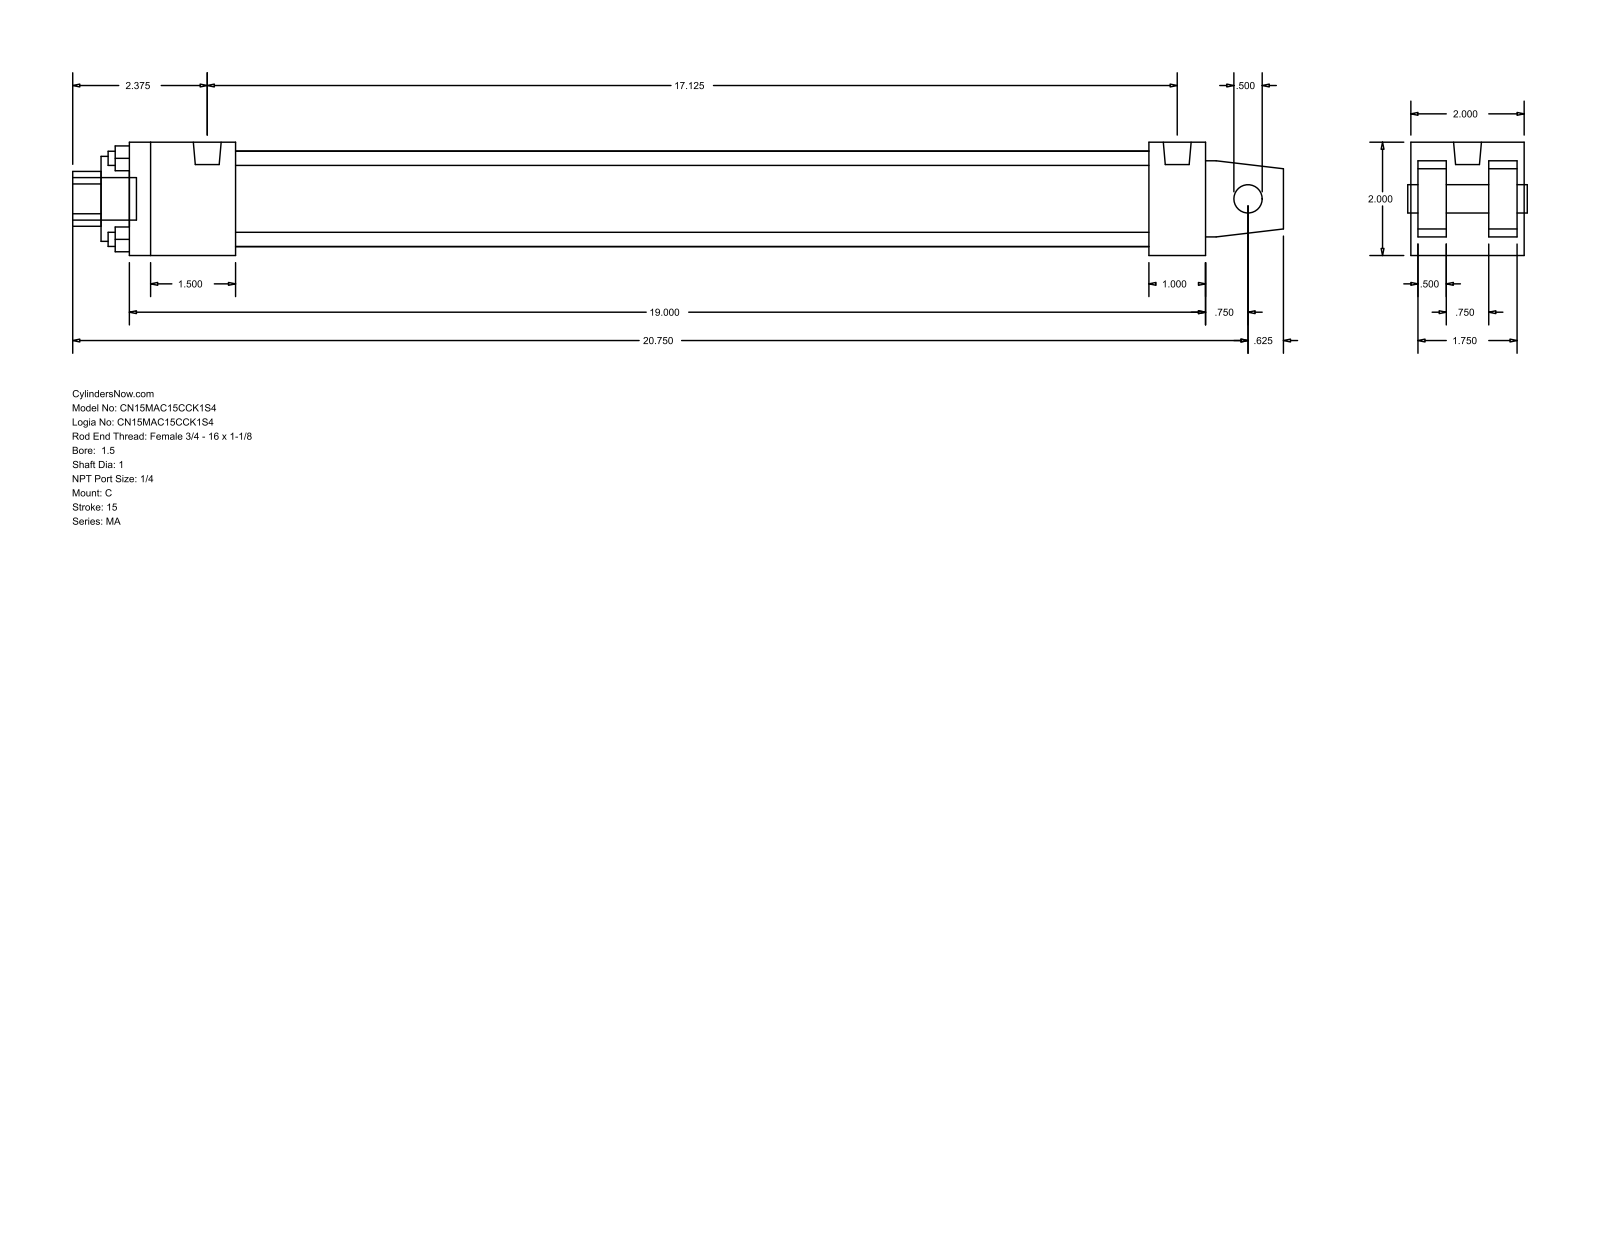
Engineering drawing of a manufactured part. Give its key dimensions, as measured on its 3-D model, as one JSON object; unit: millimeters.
{"part_name": "MA_C__0150_1", "step_written_by": "GSSL Pune (CONFIG_CONTROL_DESIGN)", "units": "millimeters", "bodies": {"solids": 0, "faces": 103, "planar": 76, "cylindrical": 27, "other": 0}, "overall_size": [542.92, 50.8, 50.8], "round_holes": [[6.35, 4], [12.7, 1], [25.4, 1], [38.1, 1], [42.93, 1]], "round_bosses_or_shafts": [[7.94, 4], [12.49, 2], [19.05, 1]], "partial_cylinders_radius": [[12.29, 1]], "face_to_face_distances": [50.8, 47.63, 12.7, 3.17, 15.87, 34.93, 31.76, 44.46, 482.6, 25.4], "hole_center_spacings": [25.68, 36.32, 51.36]}
